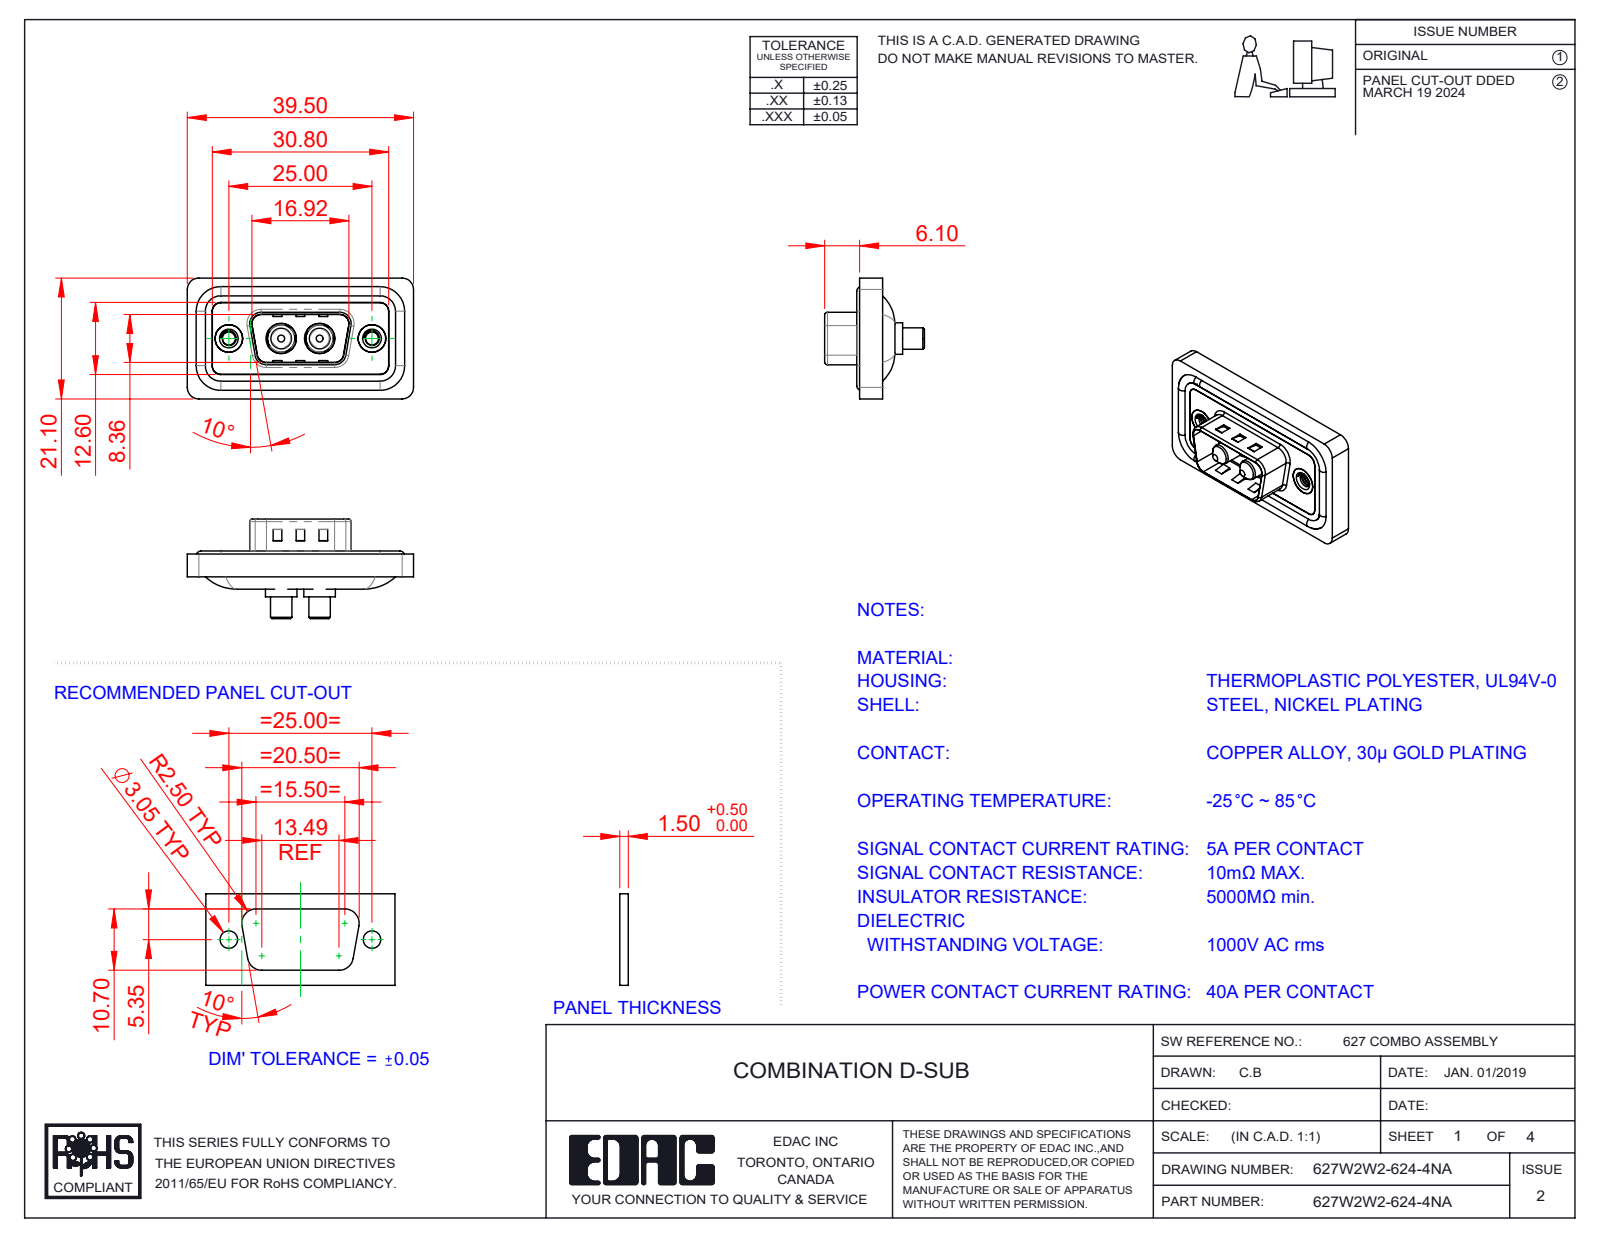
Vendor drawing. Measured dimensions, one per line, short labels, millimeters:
name: 627Combo Threaded Rivet_A; Power Pin_40A S; 627Combo Shell Rear_09 Contacts; 627Combo Shell Front_09 Contacts (+3 more)
written by: SolidWorks 2023 (CONFIG_CONTROL_DESIGN)
unit: mm
bodies: 11 solids, 487 faces (165 planar, 220 cylindrical, 102 other)
size: 39.5 × 21.1 × 17.4
volume: 4 499 mm³; area: 7 003 mm²
holes: 2× ⌀2.26, 2× ⌀4, 2× ⌀4.8, 2× ⌀4.85, 2× ⌀5, 2× ⌀5.3
bosses: 4× ⌀1.6, 2× ⌀5.5, 2× ⌀5.2, 2× ⌀4.9, 2× ⌀4.75, 2× ⌀3.75, 2× ⌀3.6
rounds: 22× R1.5, 18× R2, 8× R0.5, 8× R1.6, 4× R0.25, 4× R0.6, 4× R0.65, 4× R0.9
face distances: 0.4, 1.1, 2.9, 3.1, 0.5, 1.6, 1.5, 2.5, 4, 0.7
hole spacings: 9.14, 15.86, 6.72, 25
